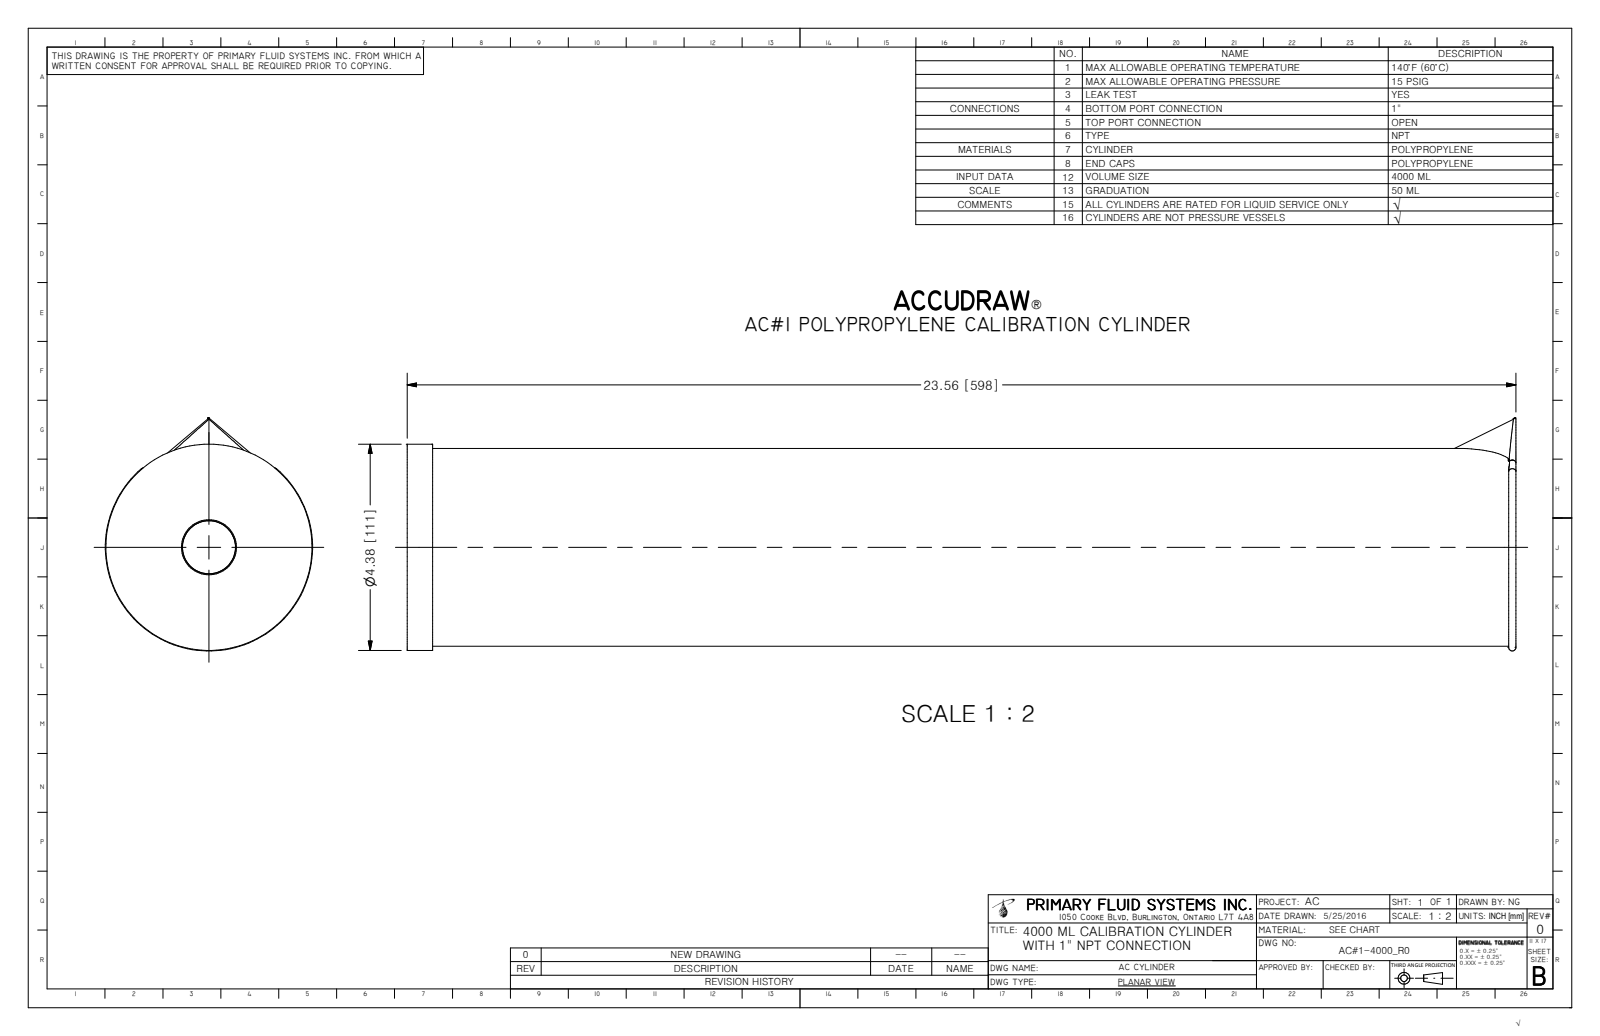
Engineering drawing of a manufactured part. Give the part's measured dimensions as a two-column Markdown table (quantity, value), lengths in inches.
| quantity | value |
| --- | --- |
| part name | AC#1-4000-F_R2 - Copy; AC-2B-4000-S; AC#1-4000-TUBE |
| STEP written by | Autodesk Inventor 2009 (AUTOMOTIVE_DESIGN) |
| units | inches |
| bodies | 2 solids, 24 faces (11 planar, 6 cylindrical, 7 other) |
| overall size | 23.559 × 4.949 × 4.404 |
| volume | 52 in³ |
| surface area | 634.1 in² |
| round holes (diameter × count) | 1.125 × 1, 1.311 × 1, 3.913 × 1 |
| round bosses / shafts (diameter × count) | 4.38 × 1, 4.2 × 1, 3.95 × 1 |
| main face-to-face distances | 0.75, 0.54, 0.21, 23.559, 23.019, 22.809, 0.574, 0.034, 0.176, 22.985 |
